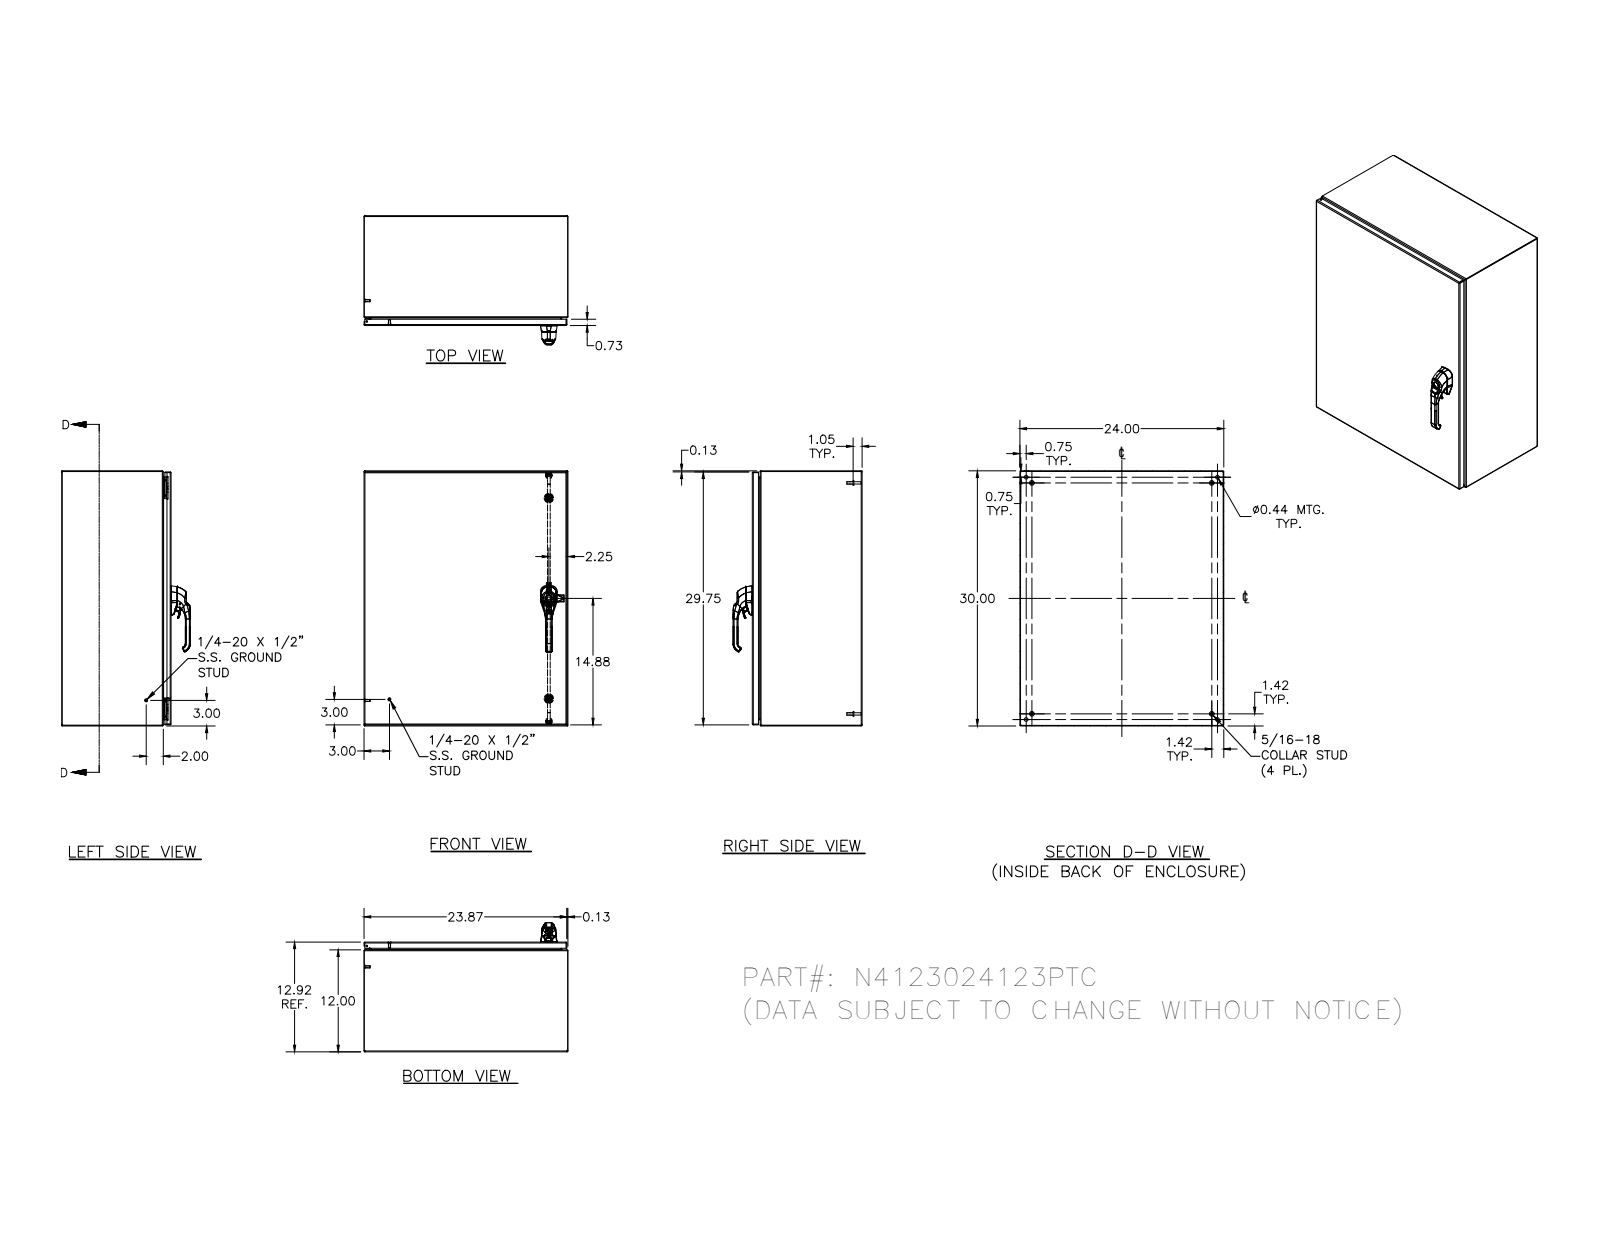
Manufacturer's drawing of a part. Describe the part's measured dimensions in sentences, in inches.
The part is named "N4123024123PTC; N4123024123PTCBKP; N41230243PTCLID; HFW328176 (+8 more)". Its 3-D file was written by "Autodesk Inventor 2011 (AUTOMOTIVE_DESIGN)". It is 49 solids with 2962 faces: 941 planar, 1101 cylindrical and 920 other. Overall it measures 30 by 24 by 15.186 inches. Its volume is 221.5 cubic inches and its surface area 6 067 square inches. Round holes: 5 of diameter 0.188, 4 of diameter 0.093, 4 of diameter 0.152, 4 of diameter 0.165, 4 of diameter 0.167, 4 of diameter 0.172, 4 of diameter 0.197, 4 of diameter 0.437, 3 of diameter 0.213, 3 of diameter 0.236, 3 of diameter 0.354, 2 of diameter 0.106. Round bosses or shafts: 10 of diameter 0.25, 4 of diameter 0.563, 4 of diameter 0.36, 4 of diameter 0.32, 4 of diameter 0.3, 4 of diameter 0.275, 4 of diameter 0.256, 4 of diameter 0.236. Partial cylindrical surfaces (rounded edges, fillets, slot ends): 180 of radius 0.02, 80 of radius 0.012, 33 of radius 0.118, 30 of radius 0.031, 26 of radius 0.05, 20 of radius 0.105, 19 of radius 0.019, 18 of radius 0.016. The main face-to-face distances are 0.074, 12.843, 23.926, 12.917, 12.769, 29.926, 23.852, 24, 30, 29.852. The hole center spacings are 25.996, 22.869, 0.017, 0.66, 26.656, 0.019, 0.177, 0.5.
